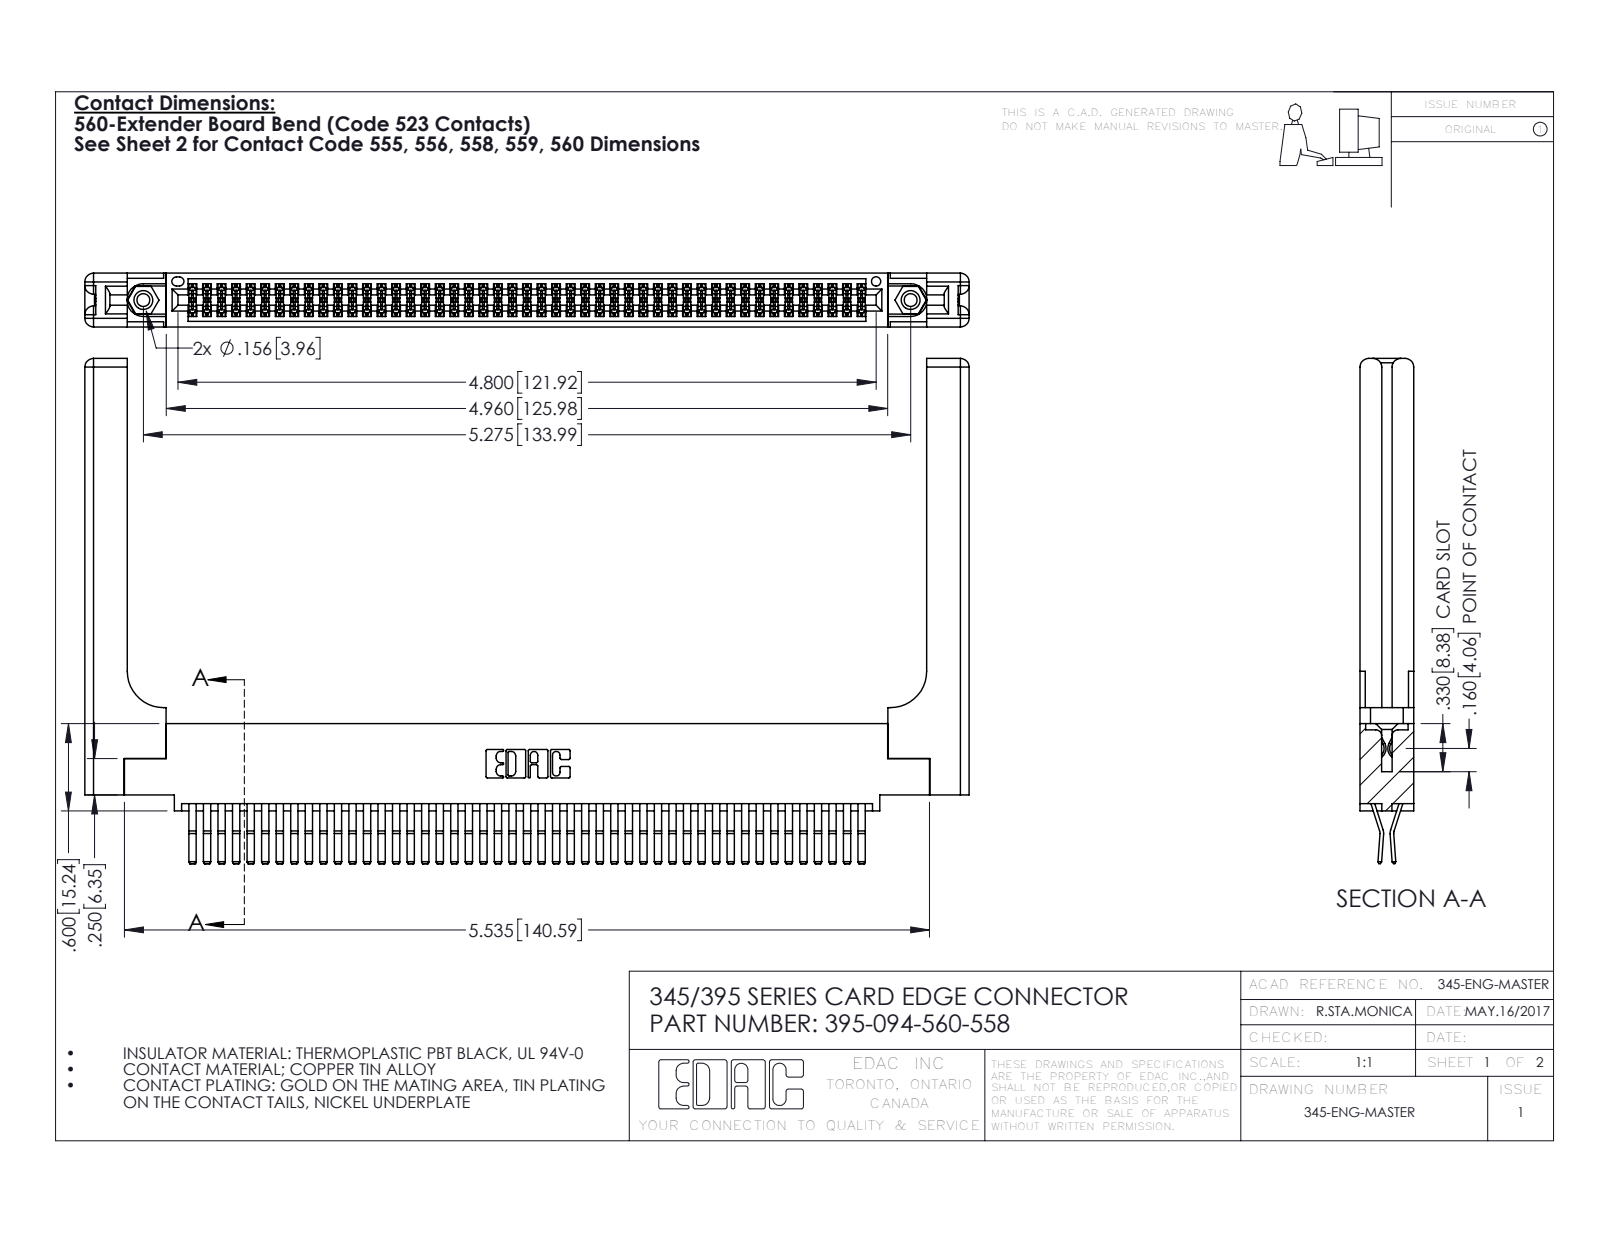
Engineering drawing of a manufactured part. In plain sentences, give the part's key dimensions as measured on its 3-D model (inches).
The part is named "345-250-001_345-250-001-102; 345-292-001_560 Tail; 395-094-560-558; 345-220-058_345-220-058 (+1 more)". Its 3-D file was written by "SolidWorks 2016 (CONFIG_CONTROL_DESIGN)". It is 99 solids with 5274 faces: 3334 planar, 1880 cylindrical and 60 other. Overall it measures 6.079 by 3.472 by 0.37 inches. Its volume is 1.468 cubic inches and its surface area 46.31 square inches. Round holes: 2 of diameter 0.089, 2 of diameter 0.125, 2 of diameter 0.156, 1 of diameter 0.064. Round bosses or shafts: 2 of diameter 0.155. Partial cylindrical surfaces (rounded edges, fillets, slot ends): 141 of radius 0.006, 22 of radius 0.01, 16 of radius 0.06, 6 of radius 0.007, 6 of radius 0.031, 3 of radius 0.026, 2 of radius 0.01, 2 of radius 0.014. The main face-to-face distances are 0.072, 0.37, 0.298, 0.025, 0.098, 0.272, 0.2, 0.225, 0.148, 0.15. The hole center spacings are 0.27, 5.039, 5.275.
